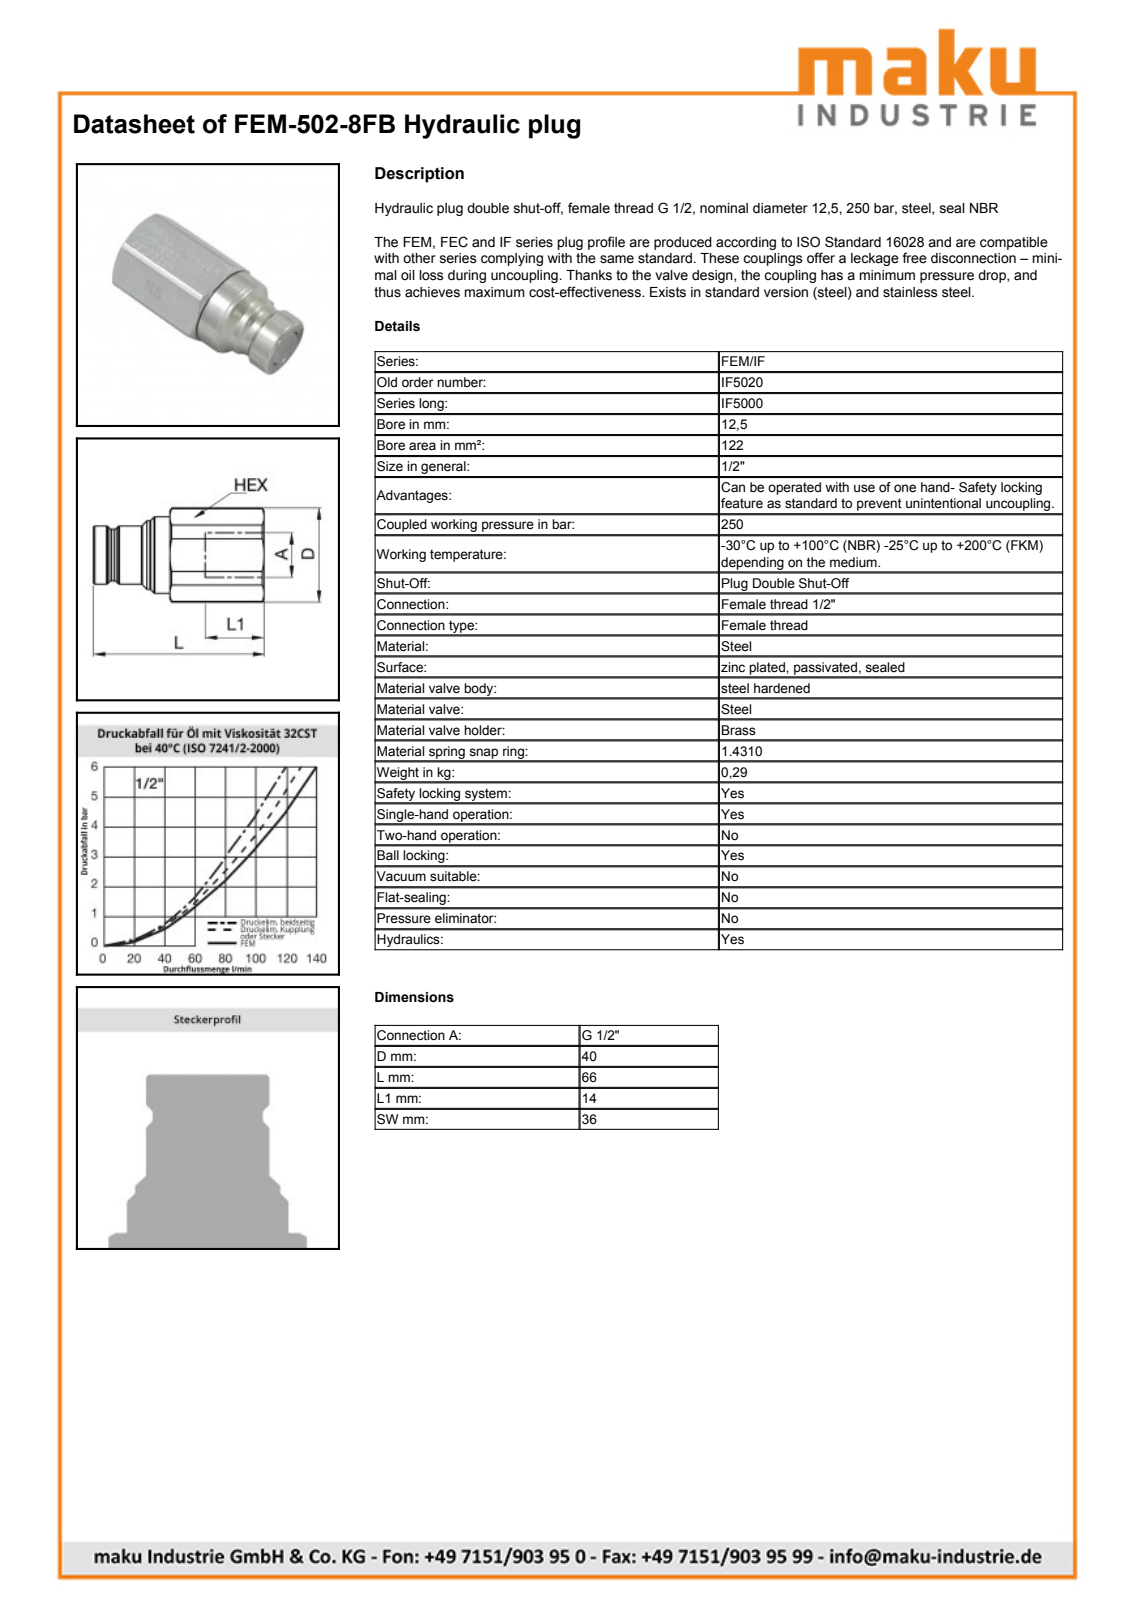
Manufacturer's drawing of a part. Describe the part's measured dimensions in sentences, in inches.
The part is named "FEM-502-8FB". Its 3-D file was written by "SolidWorks 2009 (AUTOMOTIVE_DESIGN)". It is 1 solid with 85 faces: 13 planar, 26 cylindrical and 46 other. Overall it measures 2.602 by 1.575 by 1.417 inches. Its volume is 3.11 cubic inches and its surface area 15.63 square inches. Round holes: 1 of diameter 0.618, 1 of diameter 0.733, 1 of diameter 1.187. Round bosses or shafts: 1 of diameter 1.22, 1 of diameter 1.201, 1 of diameter 1.181, 1 of diameter 0.965, 1 of diameter 0.866, 1 of diameter 0.612. Partial cylindrical surfaces (rounded edges, fillets, slot ends): 1 of radius 0.787. The main face-to-face distances are 1.417, 1.26, 0.626, 0.634, 1.343, 1.968, 2.602, 1.34, 1.966, 2.6.
